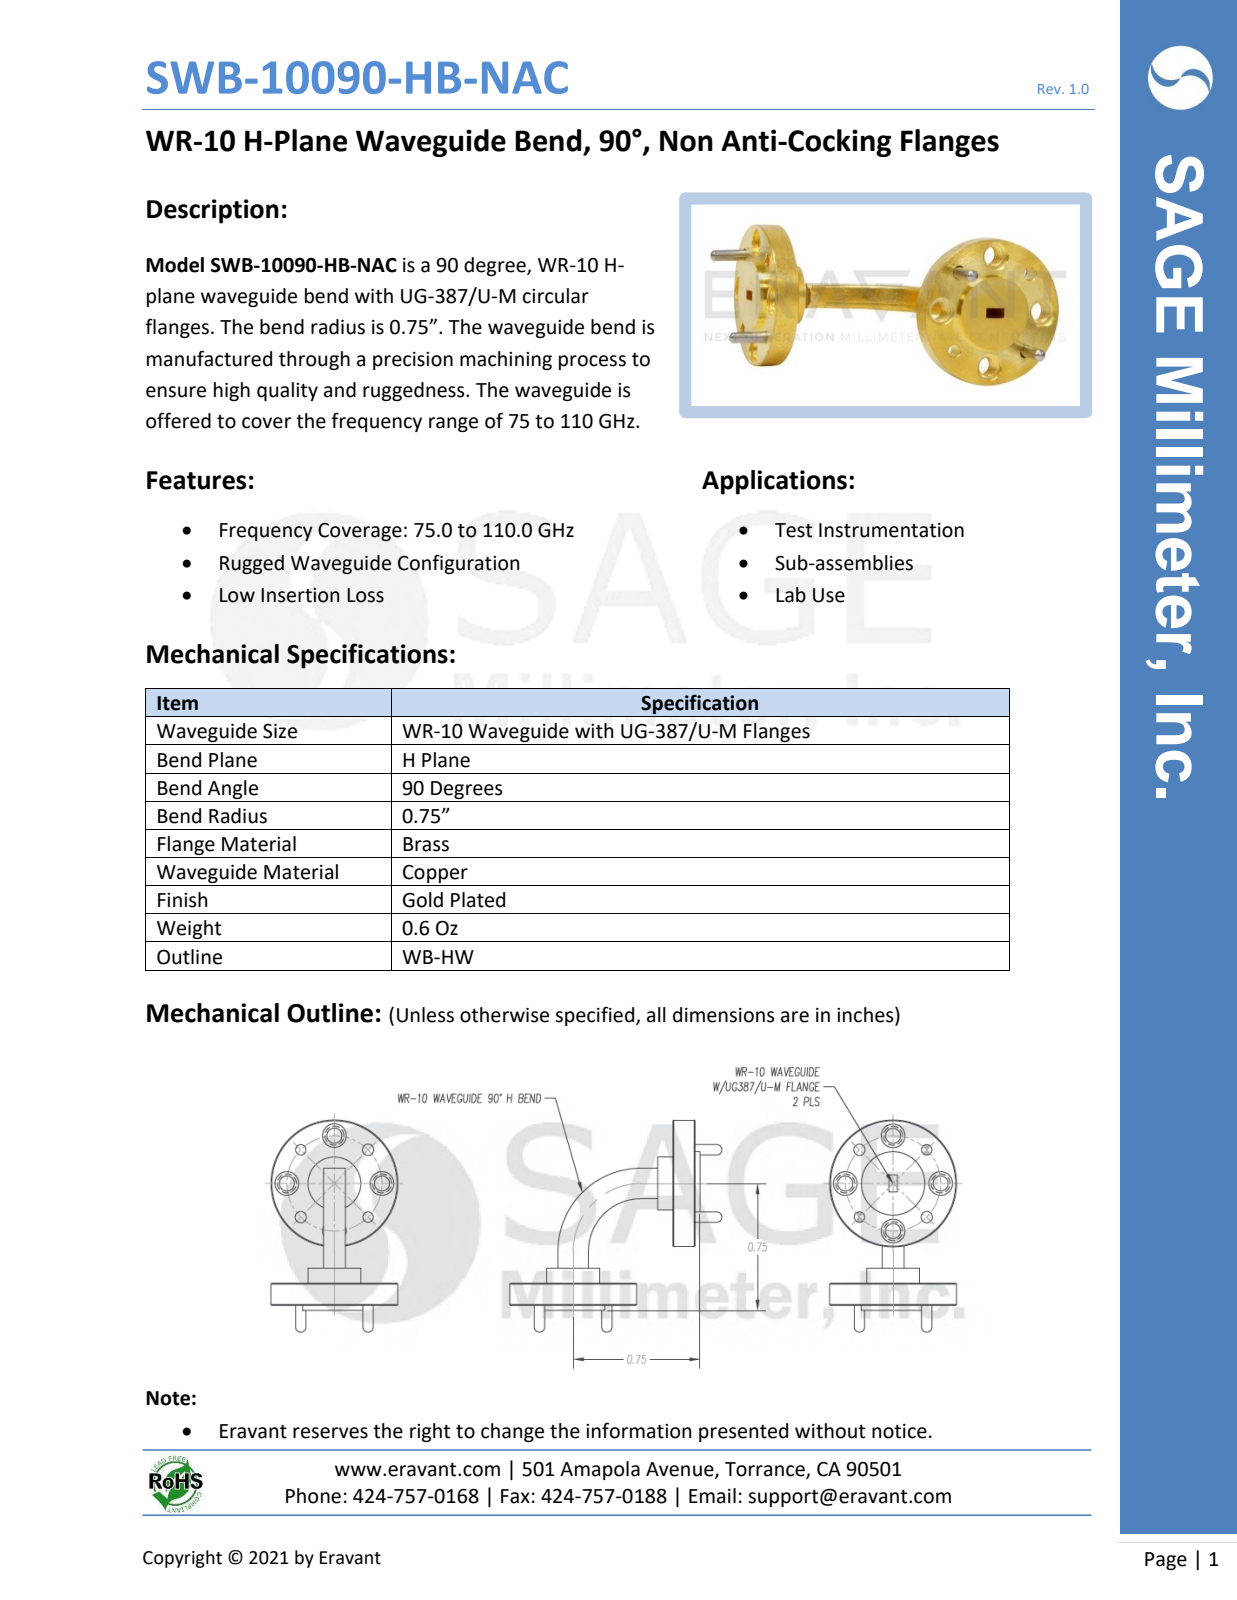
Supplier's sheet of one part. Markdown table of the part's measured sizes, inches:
| quantity | value |
| --- | --- |
| part name | SWB-10XXX-H2 |
| STEP written by | SolidWorks 2013 (CONFIG_CONTROL_DESIGN) |
| units | inches |
| bodies | 5 solids, 152 faces (40 planar, 72 cylindrical, 40 other) |
| overall size | 1.278 × 1.277 × 0.75 |
| volume | 0.145 in³ |
| surface area | 4.01 in² |
| round holes (diameter × count) | 0.089 × 8, 0.14 × 8, 0.06 × 4, 0.067 × 4 |
| round bosses / shafts (diameter × count) | 0.063 × 4, 0.75 × 2, 0.35 × 2, 0.375 × 1, 0.375 × 1 |
| partial cylindrical surfaces (radius × count) | 0.41 × 1, 0.45 × 1, 0.55 × 1, 0.59 × 1 |
| main face-to-face distances | 0.13, 0.05, 0.1, 0.23, 0.04, 0.09, 0.09, 0.04, 0.03, 0.16 |
| hole center spacings | 0.215, 0.398, 0.519, 0.52, 0.562, 0.563, 0.398 |
